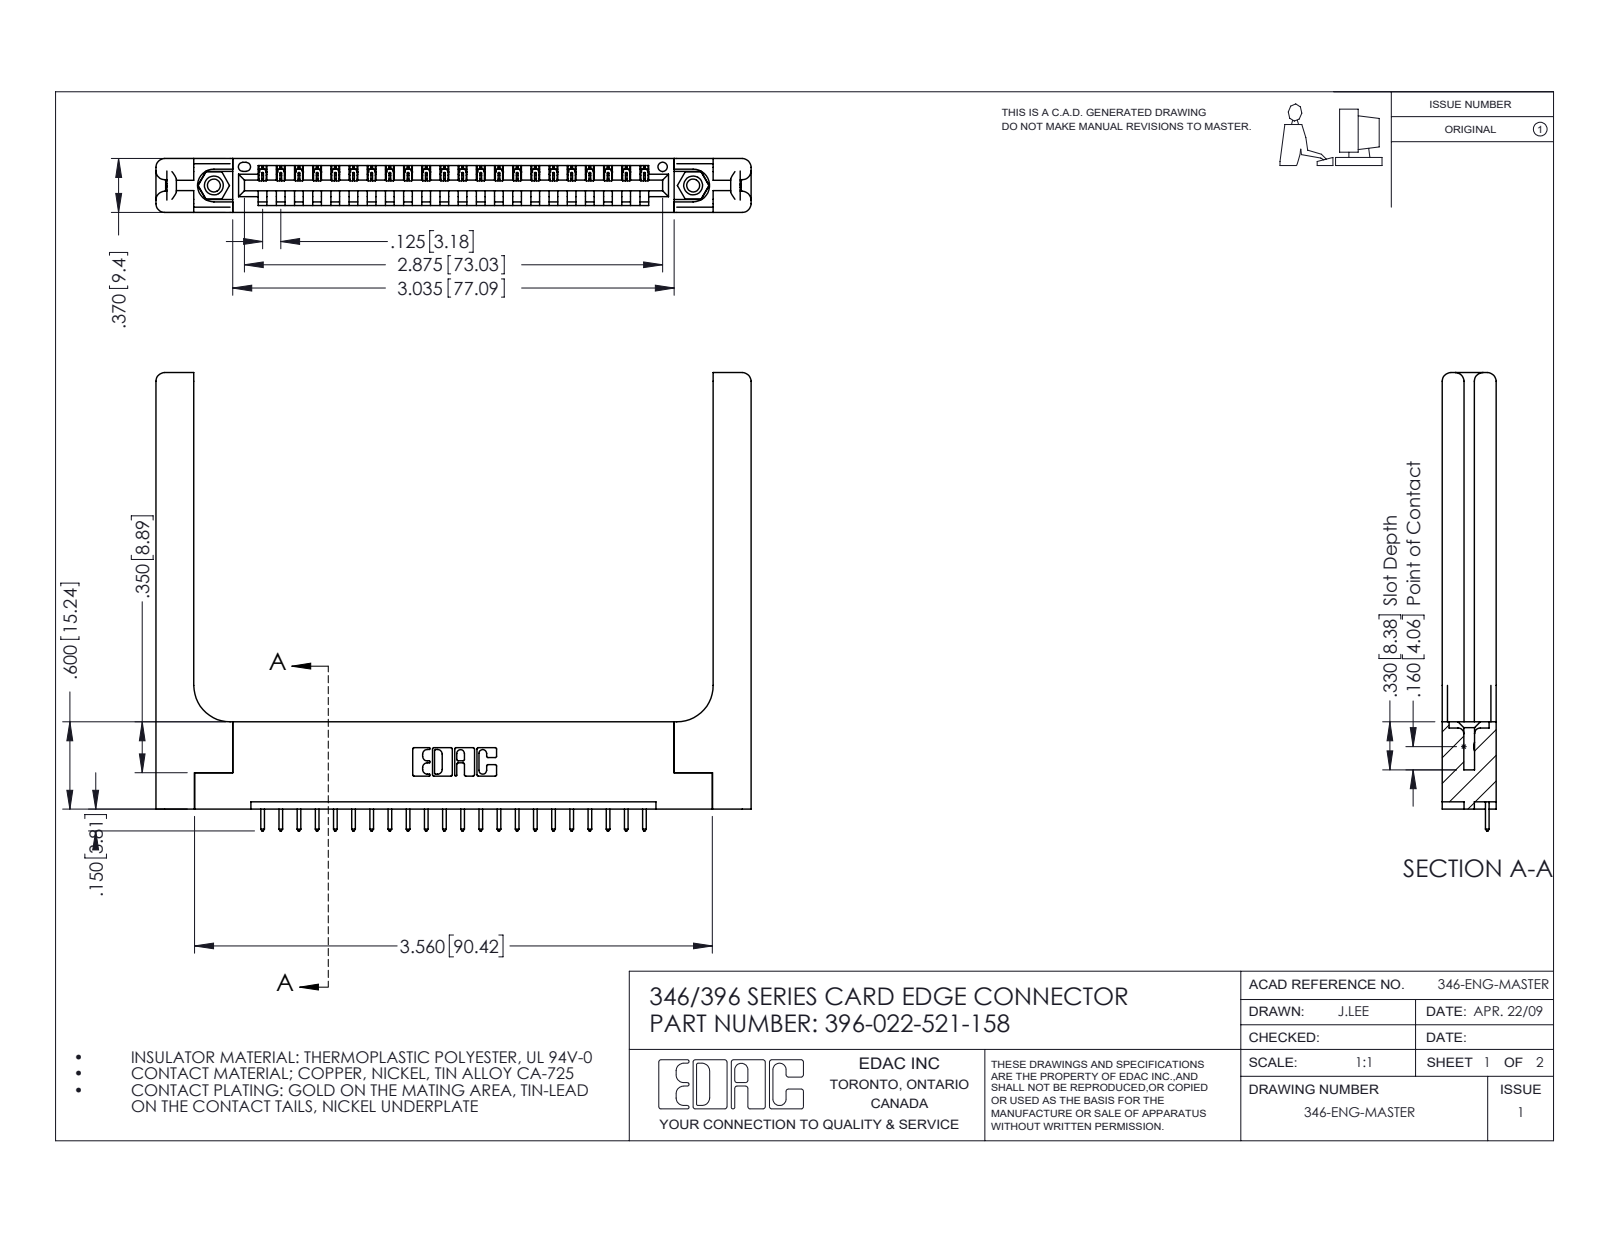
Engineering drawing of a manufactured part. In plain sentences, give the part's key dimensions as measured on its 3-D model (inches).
The part is named "346 Part_Flush Mounting Lugs - 0.156 Dia-TH; 345-250-001_345-250-001-102; 396-022-521-158; 346-220-058_345-220-058 (+1 more)". Its 3-D file was written by "SolidWorks 2016 (CONFIG_CONTROL_DESIGN)". It is 27 solids with 1654 faces: 1104 planar, 490 cylindrical and 60 other. Overall it measures 4.091 by 3.15 by 0.37 inches. Its volume is 1.054 cubic inches and its surface area 26.17 square inches. Round holes: 2 of diameter 0.089, 2 of diameter 0.125, 2 of diameter 0.156, 1 of diameter 0.064. Round bosses or shafts: 2 of diameter 0.155. Partial cylindrical surfaces (rounded edges, fillets, slot ends): 44 of radius 0.006, 44 of radius 0.01, 22 of radius 0.01, 16 of radius 0.06, 6 of radius 0.007, 6 of radius 0.031, 3 of radius 0.026, 2 of radius 0.03. The main face-to-face distances are 0.37, 0.072, 0.15, 0.148, 0.048, 0.322, 0.25, 0.298, 0.025, 0.102. The hole center spacings are 0.246, 3.087, 3.295.
